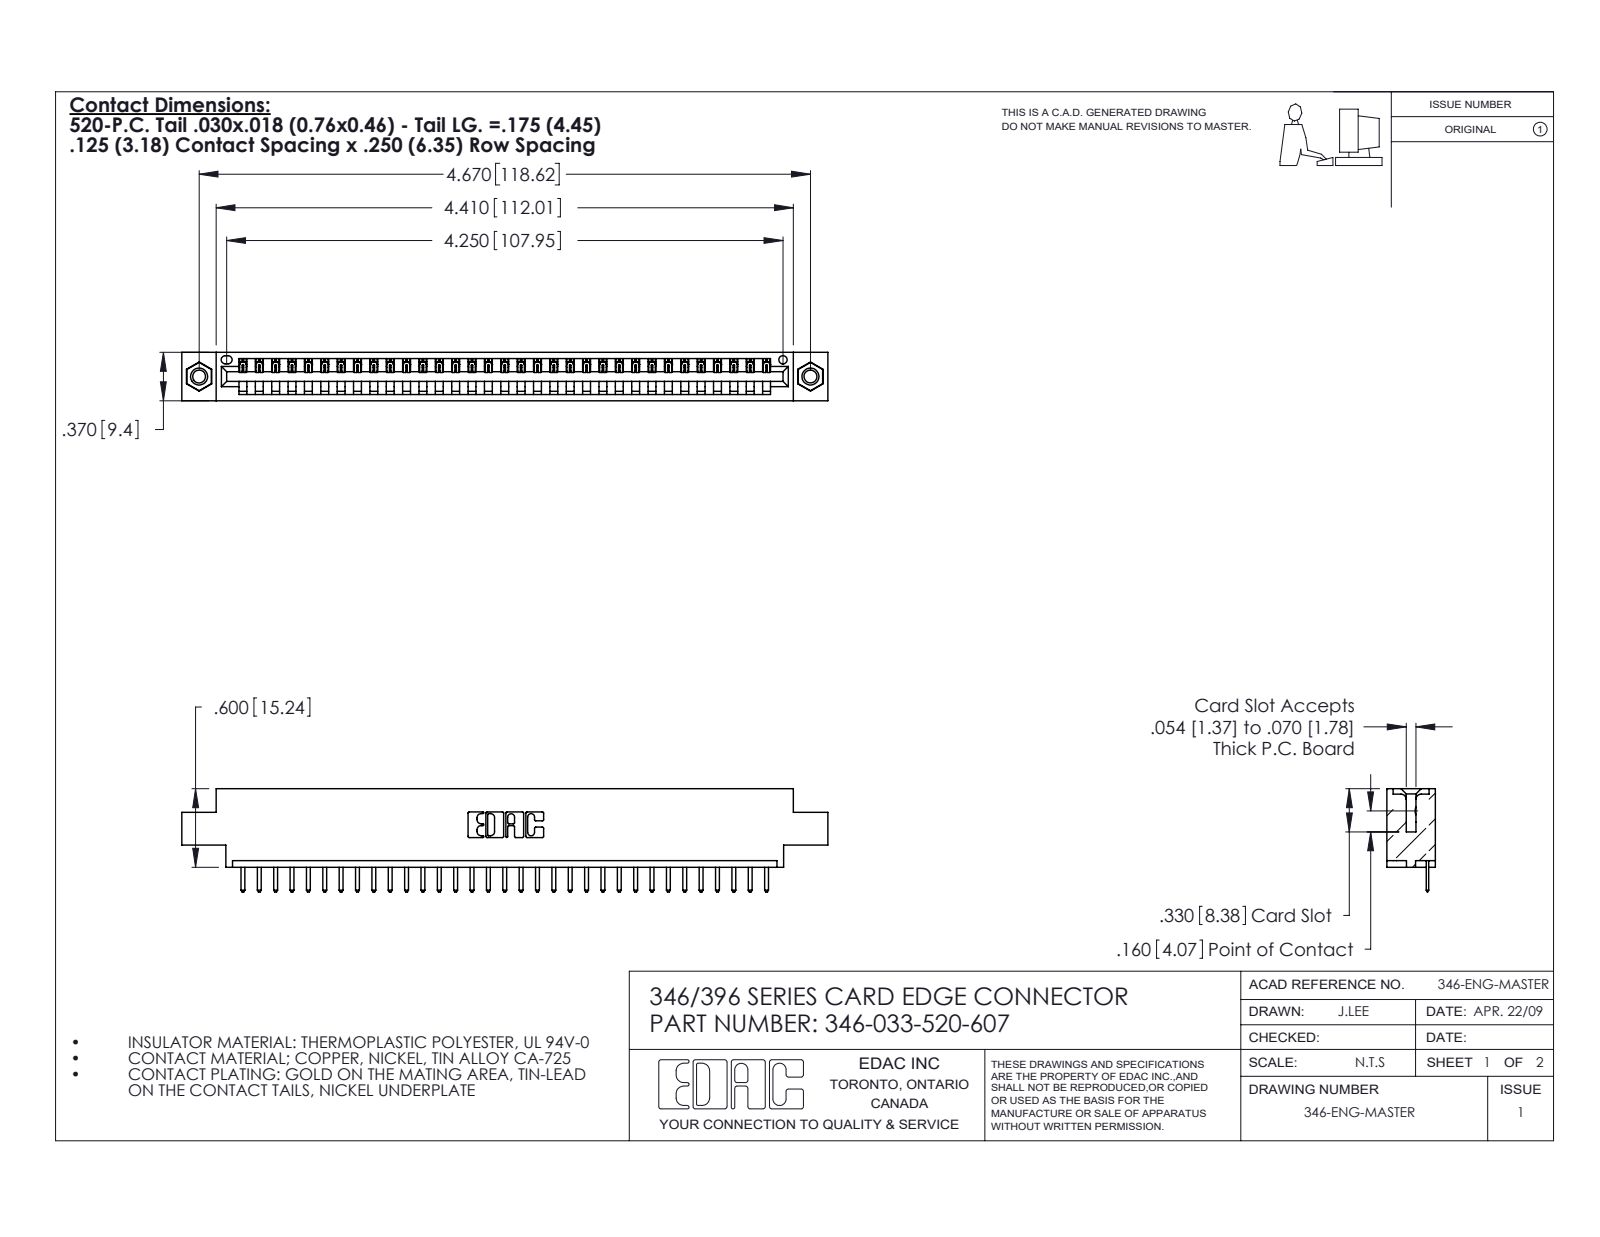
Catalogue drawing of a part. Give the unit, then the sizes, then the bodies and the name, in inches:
Units: inches
Overall size (bounding box): 4.935 × 0.788 × 0.37
Round holes (diameter × count): ⌀0.098 ×2, ⌀0.125 ×2, ⌀0.156 ×2, ⌀0.064 ×1
Round bosses / shafts (diameter × count): ⌀0.155 ×2
Partial cylindrical surfaces — rounded edges, fillets, slot ends (radius × count): R0.01 ×68, R0.006 ×66, R0.01 ×22, R0.007 ×6, R0.031 ×6, R0.026 ×3, R0.031 ×2, R0.04 ×2
Main face-to-face distances: 0.048, 0.322, 0.37, 0.25, 0.222, 0.148, 0.1, 0.174, 0.072, 0.298
Hole centre spacings: 0.246, 4.462, 4.67
Volume: 0.712 in³ · Surface area: 22.28 in²
Bodies: 36 solids, 2232 faces (1498 planar, 718 cylindrical, 16 other)
Part name (STEP PRODUCT): 345-292-001_345-293-120; 346-033-520-607; 346 Part_0.170 Offset - 0.156 Dia-TI; 345-250-001_345-250-005-103
STEP written by: SolidWorks 2020 (CONFIG_CONTROL_DESIGN)
